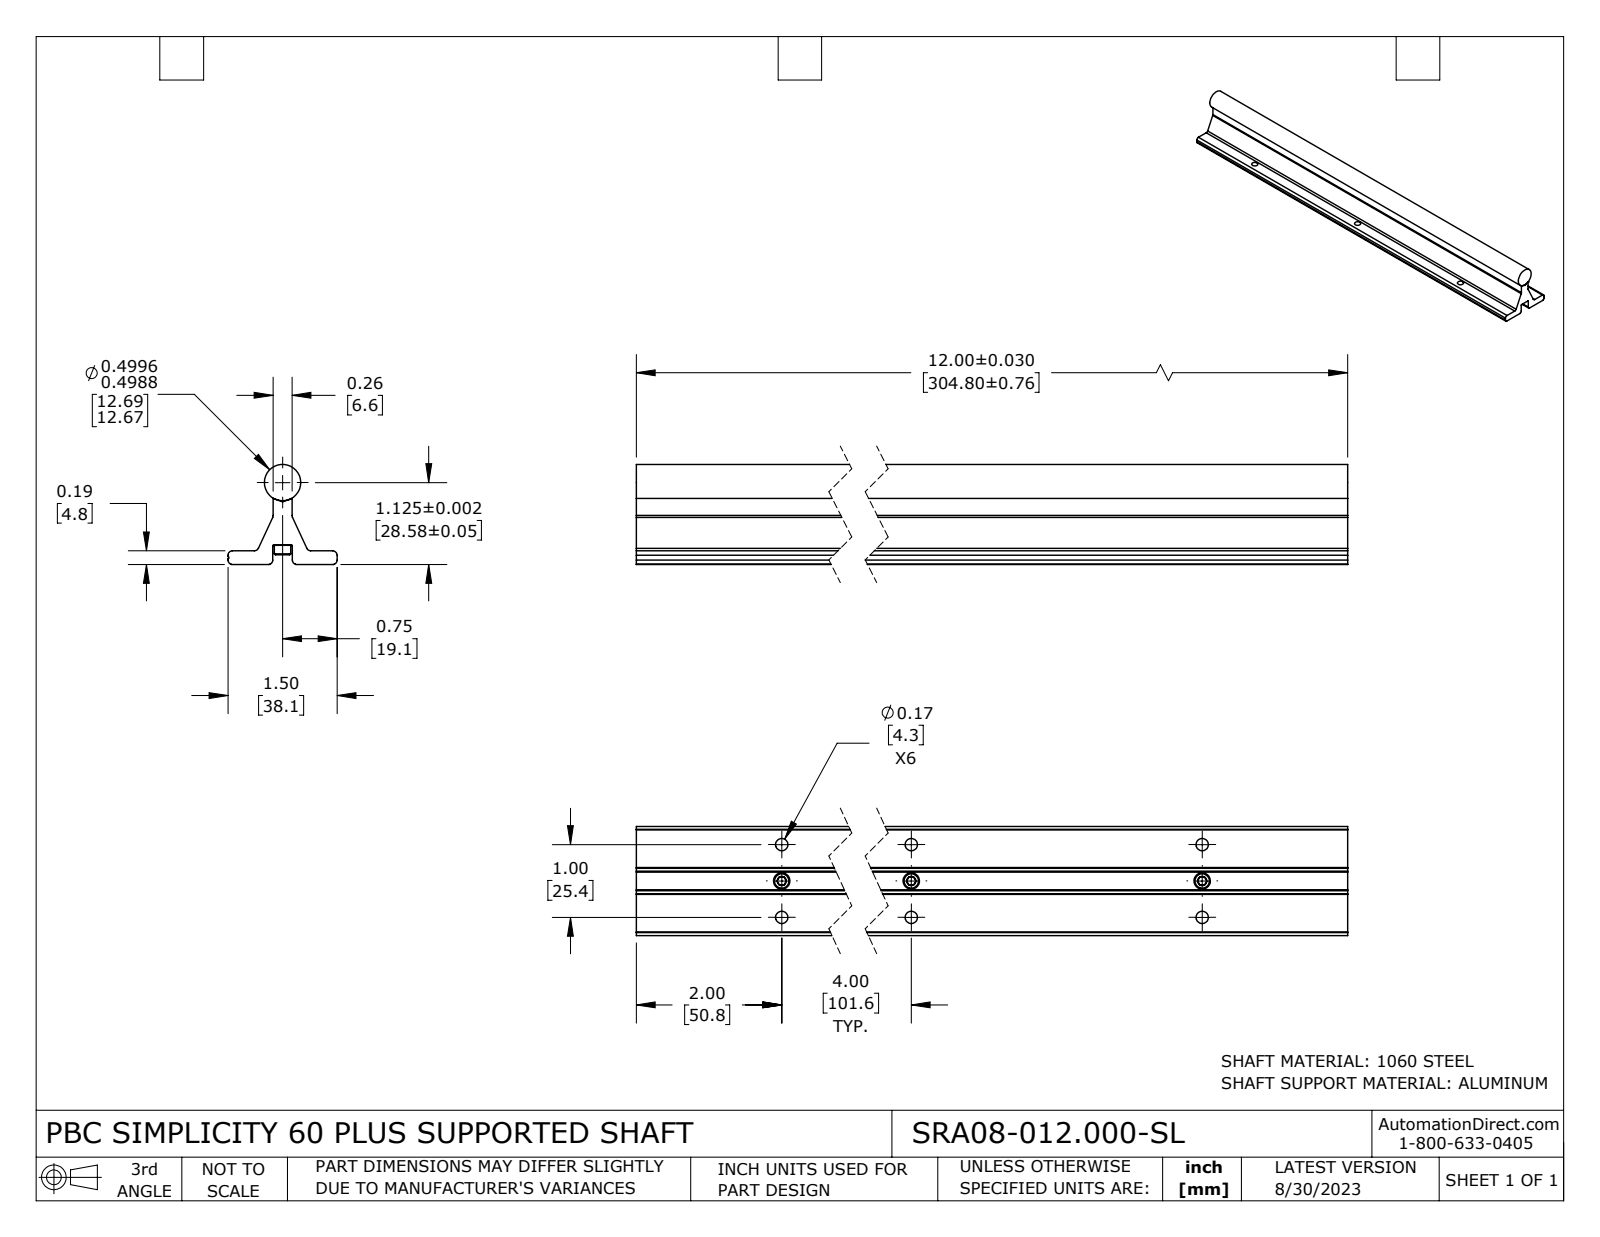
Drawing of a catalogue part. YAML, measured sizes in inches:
part_name: "SRA08-012.000-SL"
step_written_by: "SolidWorks 2021 (CONFIG_CONTROL_DESIGN)"
units: inches
bodies: {solids: 5, faces: 161, planar: 60, cylindrical: 56, other: 45}
overall_size: [12, 1.5, 1.375]
volume: 8.191
surface_area: 81.83
round_holes:
  - {diameter: 0.17, count: 9}
  - {diameter: 0.116, count: 3}
  - {diameter: 0.156, count: 3}
round_bosses_or_shafts:
  - {diameter: 0.226, count: 3}
  - {diameter: 0.138, count: 3}
  - {diameter: 0.5, count: 1}
partial_cylinders:
  - {radius: 0.06, count: 8}
  - {radius: 0.015, count: 2}
  - {radius: 0.062, count: 1}
  - {radius: 0.063, count: 1}
face_to_face_distances: [0.187, 0.27, 0.265, 0.083, 0.26, 0.615, 0.62, 0.88, 0.885, 12]
hole_center_spacings: [4.031, 0.5, 4, 4.123, 8.016, 1, 8, 8.062]
